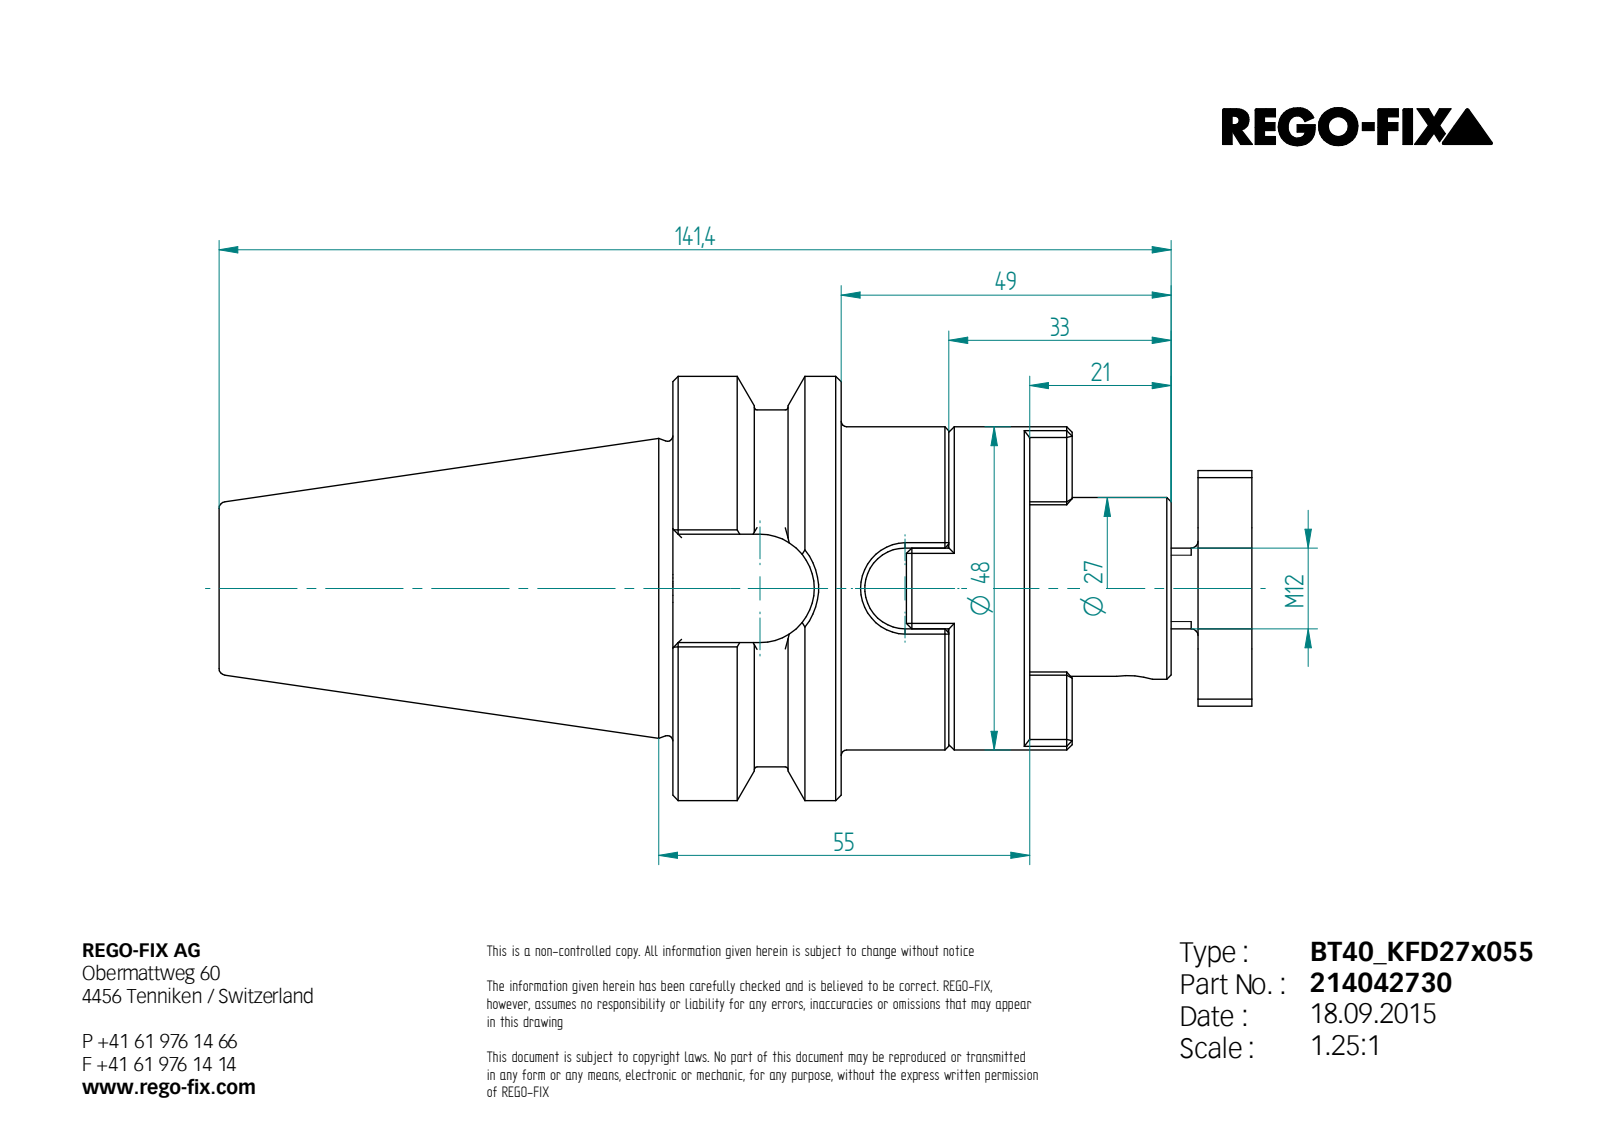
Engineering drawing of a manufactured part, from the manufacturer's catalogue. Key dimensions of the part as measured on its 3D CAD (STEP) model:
STEP written by: Unknown (AUTOMOTIVE_DESIGN)
Units: millimetres
Bodies: 3 solids, 215 faces (126 planar, 35 cylindrical, 54 other)
Overall size (bounding box): 153.4 × 63 × 63
Volume: 185 528 mm³ · Surface area: 39 000 mm²
Round holes (diameter × count): ⌀10.11 ×1, ⌀13 ×1, ⌀13.84 ×1, ⌀17 ×1, ⌀27 ×1
Round bosses / shafts (diameter × count): ⌀63 ×1, ⌀53 ×1, ⌀48 ×1, ⌀26.4 ×1, ⌀12 ×1
Partial cylindrical surfaces — rounded edges, fillets, slot ends (radius × count): R0.5 ×4, R3 ×4, R3.5 ×2, R6 ×1, R8.05 ×1, R17.5 ×1
Main face-to-face distances: 12, 25, 53, 41, 16, 28, 33, 8, 86, 61
